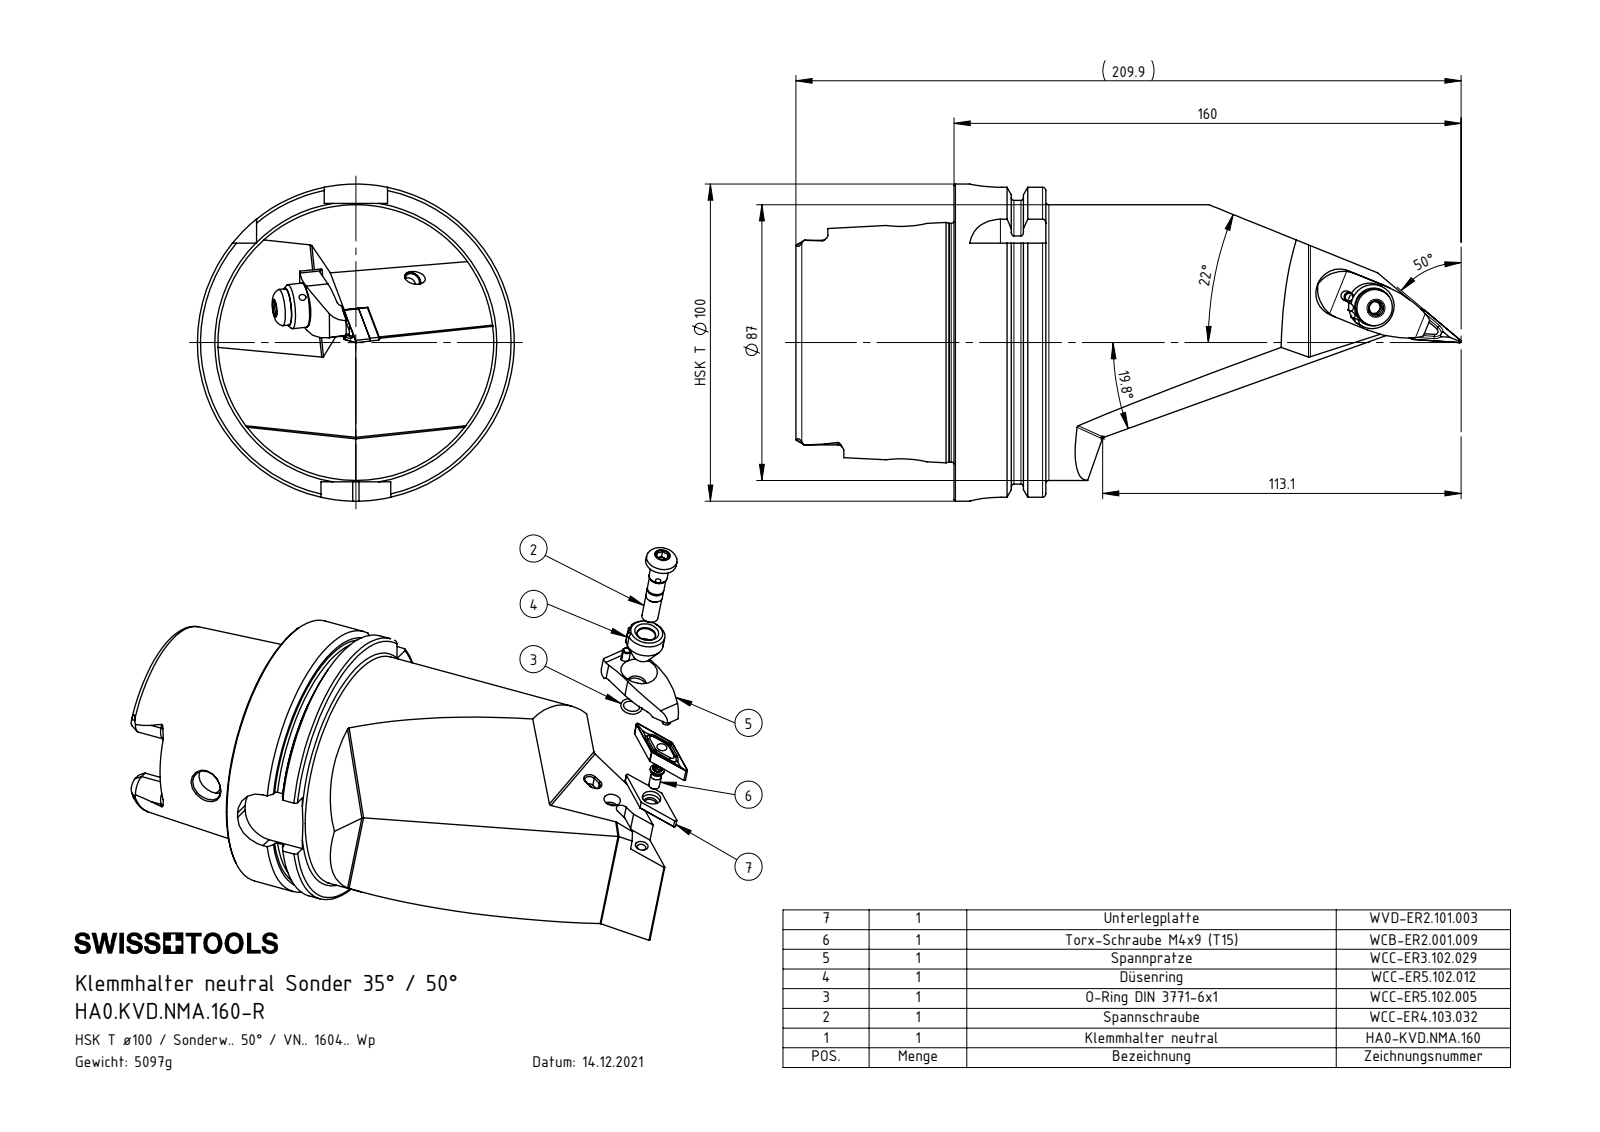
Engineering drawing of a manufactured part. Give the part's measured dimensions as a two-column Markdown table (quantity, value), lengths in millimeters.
| quantity | value |
| --- | --- |
| part name | 0-K.D.NMA.160-R; ISO 13337 - 3 x 12_PreviewCfg; WVD-ER2.101.003_A; WCC-ER5.102.005_A (+7 more) |
| STEP written by | SolidWorks 2017 (AUTOMOTIVE_DESIGN) |
| units | millimeters |
| bodies | 11 solids, 471 faces (126 planar, 156 cylindrical, 189 other) |
| overall size | 209.9 × 100 × 100 |
| volume | 648 782 mm³ |
| surface area | 80 943 mm² |
| round holes (diameter × count) | 2 × 3, 5 × 3, 7 × 2, 12 × 2, 2.4 × 1, 3 × 1, 3.3 × 1, 3.8 × 1, 4.95 × 1, 6 × 1, 6.2 × 1, 6.9 × 1 |
| round bosses / shafts (diameter × count) | 6 × 2, 4 × 2, 3 × 2, 100 × 1, 91.95 × 1, 87 × 1, 75.26 × 1, 14 × 1 |
| partial cylindrical surfaces (radius × count) | 0.34 × 6, 0.59 × 6, 1.9 × 6, 0.8 × 5, 0.4 × 4, 4.88 × 4, 10 × 4, 1.5 × 3 |
| main face-to-face distances | 12.45, 28.95, 16.5, 49.9, 62.35, 78.85, 87.8, 78.2, 28.3, 15.85 |
| hole center spacings | 8.02, 8.2, 19.3, 8.01, 19.12, 27.32, 27.33 |
